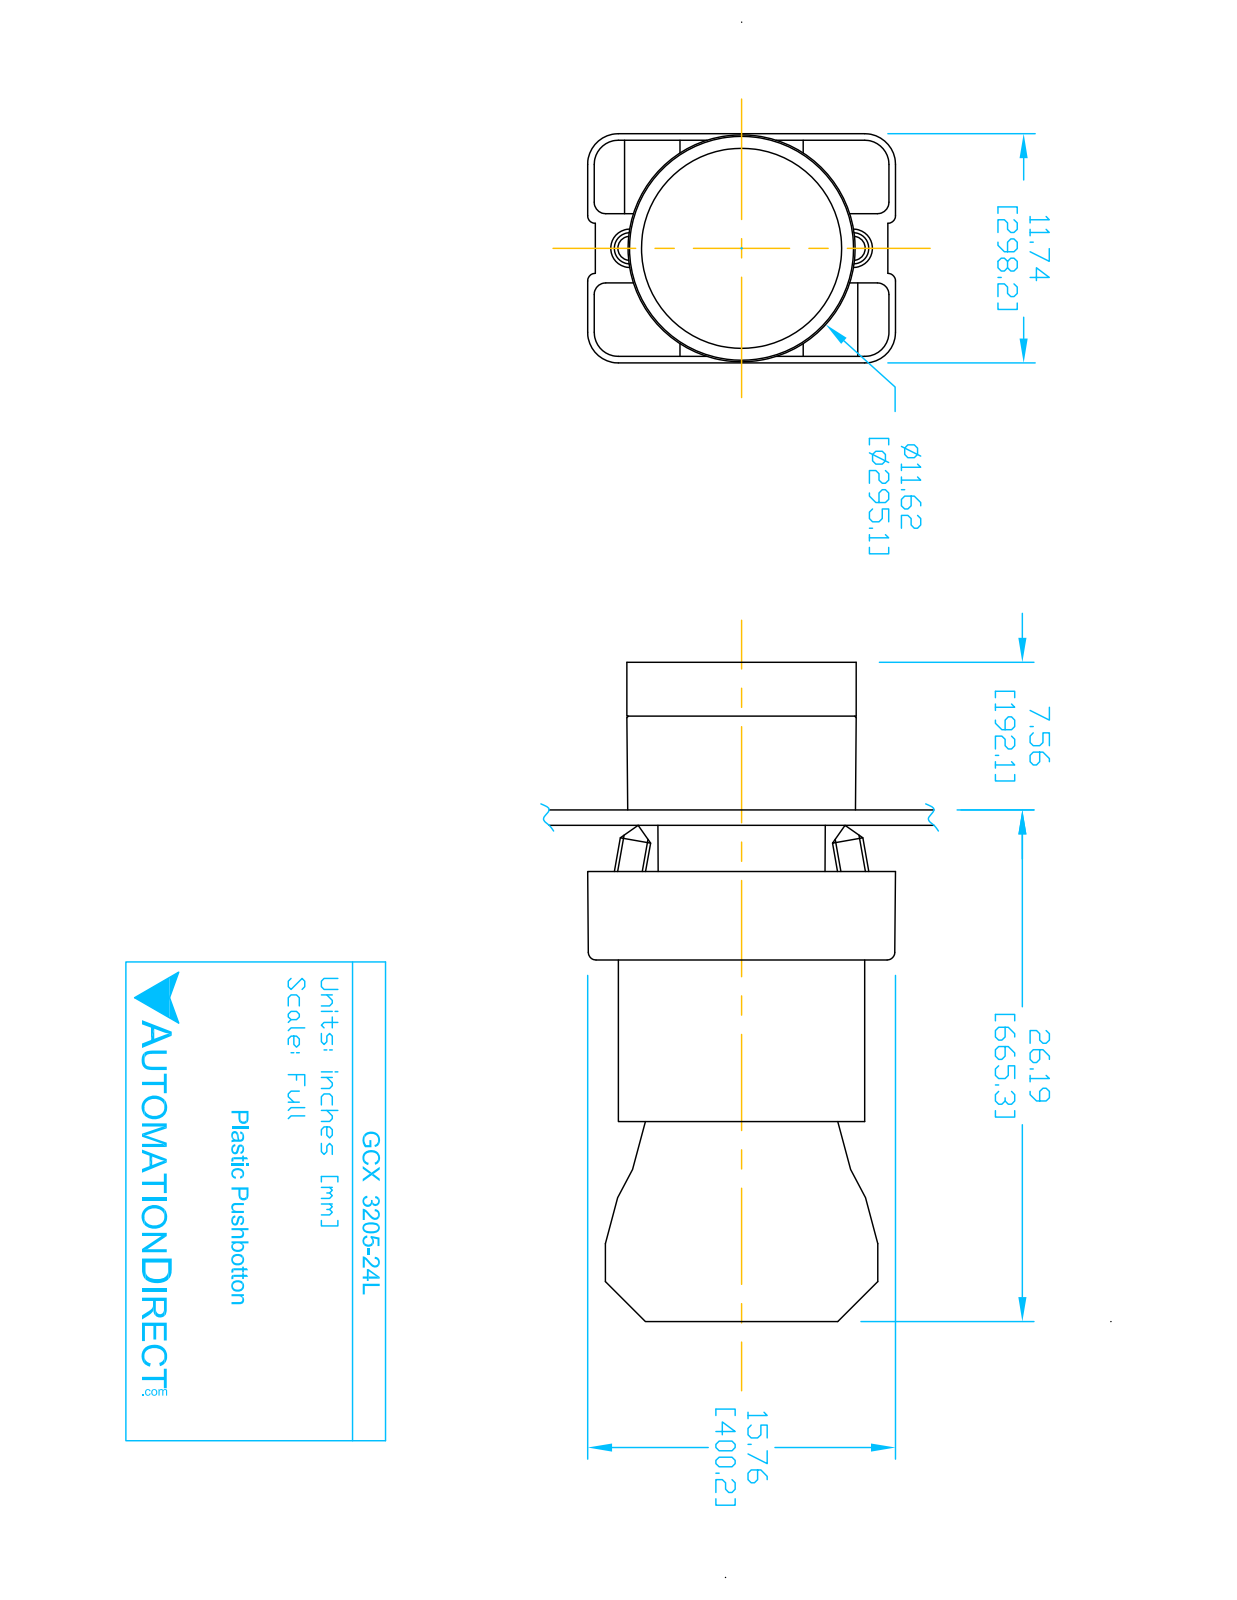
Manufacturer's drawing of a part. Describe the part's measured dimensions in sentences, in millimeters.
The part is named "GCX3205L OPERATOR; ecx1040; ECX1050; GCX3205-24L (+1 more)". Its 3-D file was written by "SolidWorks 2016 (AUTOMOTIVE_DESIGN)". It is 8 solids with 431 faces: 252 planar, 148 cylindrical and 31 other. Overall it measures 84.3 by 40.2 by 29.9 millimeters. Its volume is 45 790 cubic millimeters and its surface area 25 010 square millimeters. Round holes: 2 of diameter 2, 2 of diameter 3.1, 2 of diameter 3.3, 1 of diameter 2.2, 1 of diameter 5, 1 of diameter 11.9, 1 of diameter 22.3, 1 of diameter 22.6, 1 of diameter 26. Round bosses or shafts: 4 of diameter 4, 1 of diameter 29.8, 1 of diameter 25.5, 1 of diameter 24, 1 of diameter 21.7, 1 of diameter 19.8, 1 of diameter 12.8. Partial cylindrical surfaces (rounded edges, fillets, slot ends): 24 of radius 1.5, 12 of radius 1, 12 of radius 3.1, 12 of radius 4, 8 of radius 1, 2 of radius 3.3, 1 of radius 0.5, 1 of radius 1.6. The main face-to-face distances are 21, 14.7, 51.3, 30.3, 29.7, 7, 58.3, 37.3, 0.8, 0.8. The hole center spacings are 6, 13.8, 12, 12.4.
